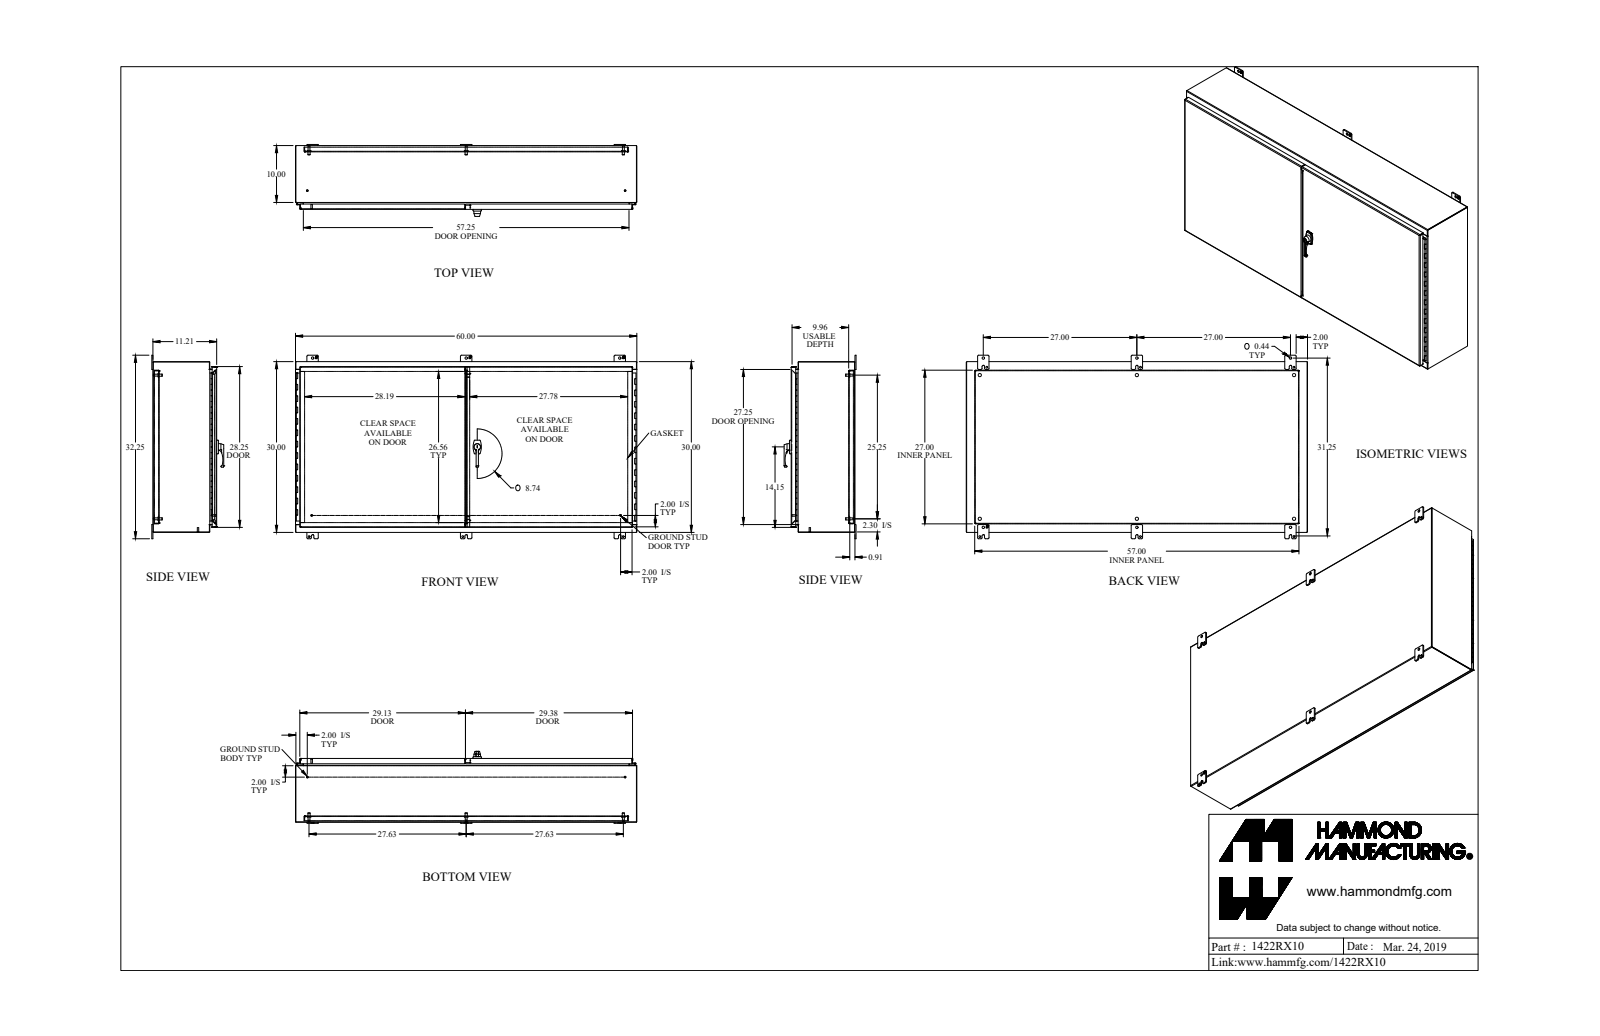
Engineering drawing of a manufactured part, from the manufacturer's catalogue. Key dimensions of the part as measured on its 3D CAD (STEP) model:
Part name (STEP PRODUCT): 1422RX10
STEP written by: SolidWorks 2019 (AUTOMOTIVE_DESIGN)
Units: inches
Bodies: 0 solids, 1717 faces (1116 planar, 483 cylindrical, 118 other)
Overall size (bounding box): 60 × 32.25 × 12.637
Round holes (diameter × count): ⌀0.304 ×10, ⌀0.307 ×7, ⌀0.313 ×6, ⌀0.437 ×6, ⌀0.563 ×6, ⌀0.218 ×4, ⌀0.445 ×4, ⌀0.215 ×3, ⌀0.11 ×2, ⌀0.127 ×2, ⌀0.156 ×2, ⌀0.187 ×2
Round bosses / shafts (diameter × count): ⌀1 ×7, ⌀0.65 ×6, ⌀0.375 ×6, ⌀0.33 ×6, ⌀0.5 ×5, ⌀0.313 ×4, ⌀0.281 ×4, ⌀0.25 ×4
Partial cylindrical surfaces — rounded edges, fillets, slot ends (radius × count): R0.188 ×38, R0.048 ×22, R0.143 ×22, R0.05 ×16, R0.036 ×14, R0.108 ×14, R0.187 ×13, R0.116 ×12
Main face-to-face distances: 0.072, 11.043, 11.115, 0.095, 0.095, 0.937, 11.138, 11.21, 10.106, 10.011
Hole centre spacings: 6, 58.7, 27, 12, 40.176, 59.613, 27.657, 58.392
